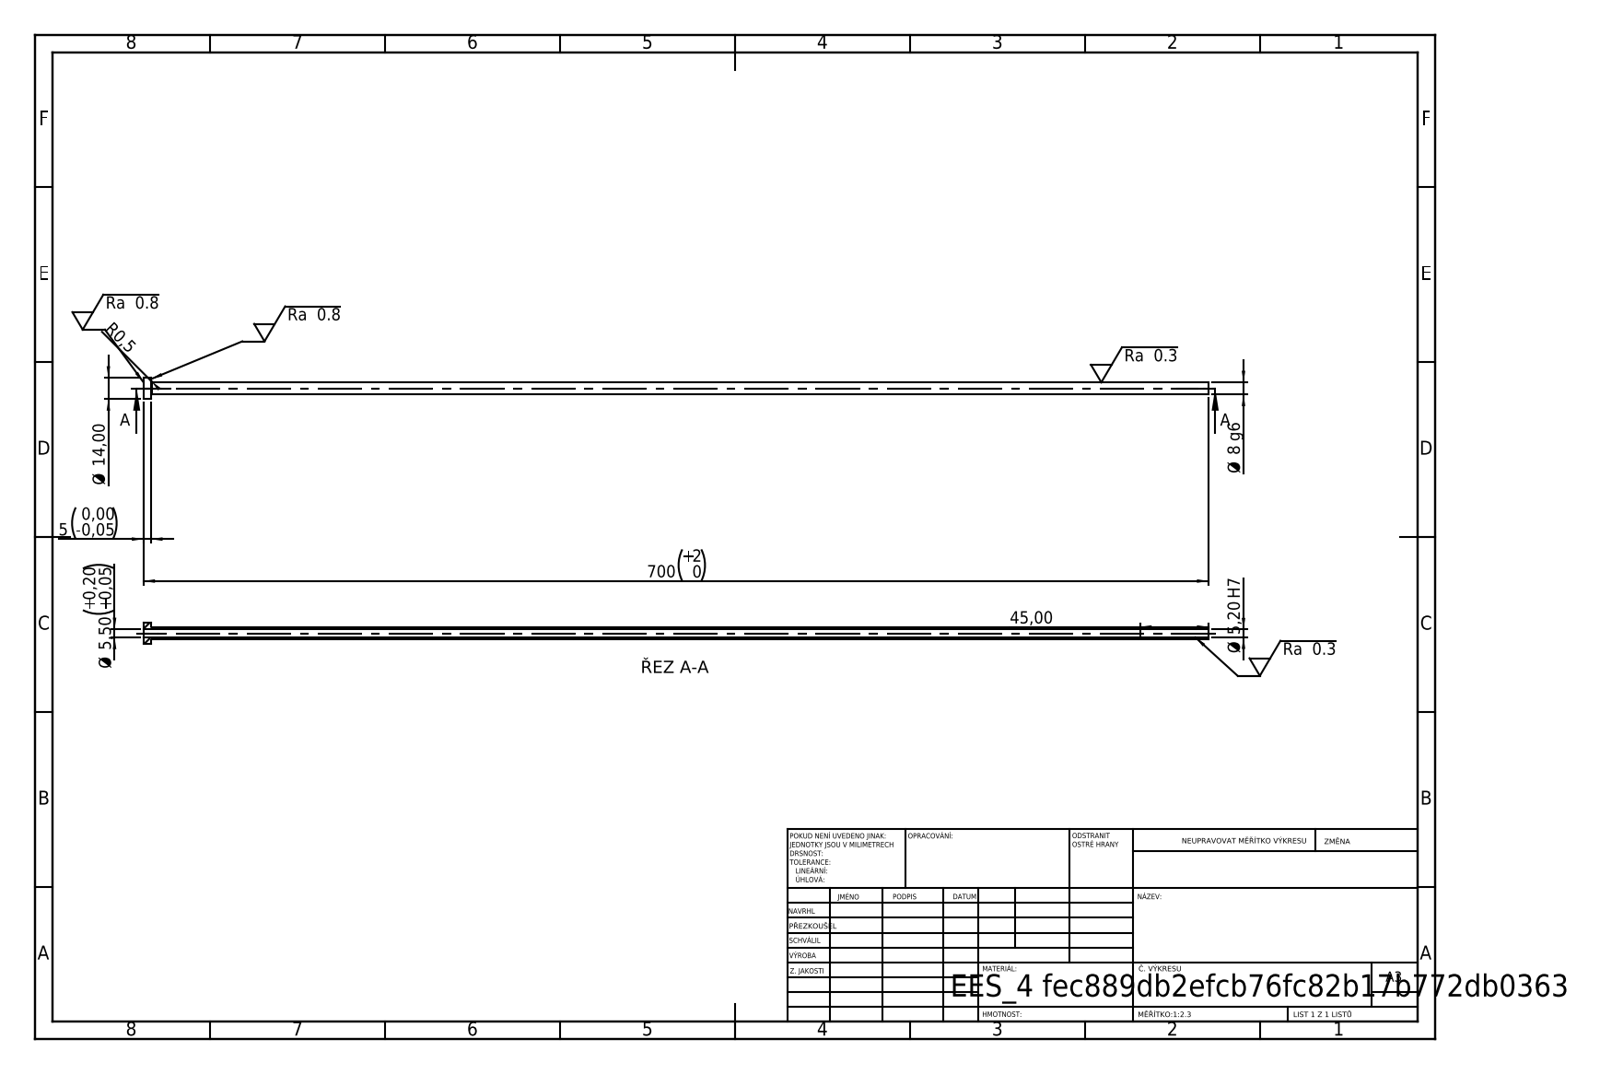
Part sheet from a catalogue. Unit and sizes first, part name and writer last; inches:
Units: inches
Overall size (bounding box): 27.559 × 0.551 × 0.551
Round holes (diameter × count): ⌀0.205 ×1, ⌀0.217 ×1
Round bosses / shafts (diameter × count): ⌀0.551 ×1, ⌀0.315 ×1
Main face-to-face distances: 0.197, 27.559, 27.362, 25.787, 25.591, 1.772
Volume: 1.171 in³ · Surface area: 46.5 in²
Bodies: 1 solid, 14 faces (4 planar, 8 cylindrical, 2 other)
STEP written by: SolidWorks 2019 (CONFIG_CONTROL_DESIGN)
